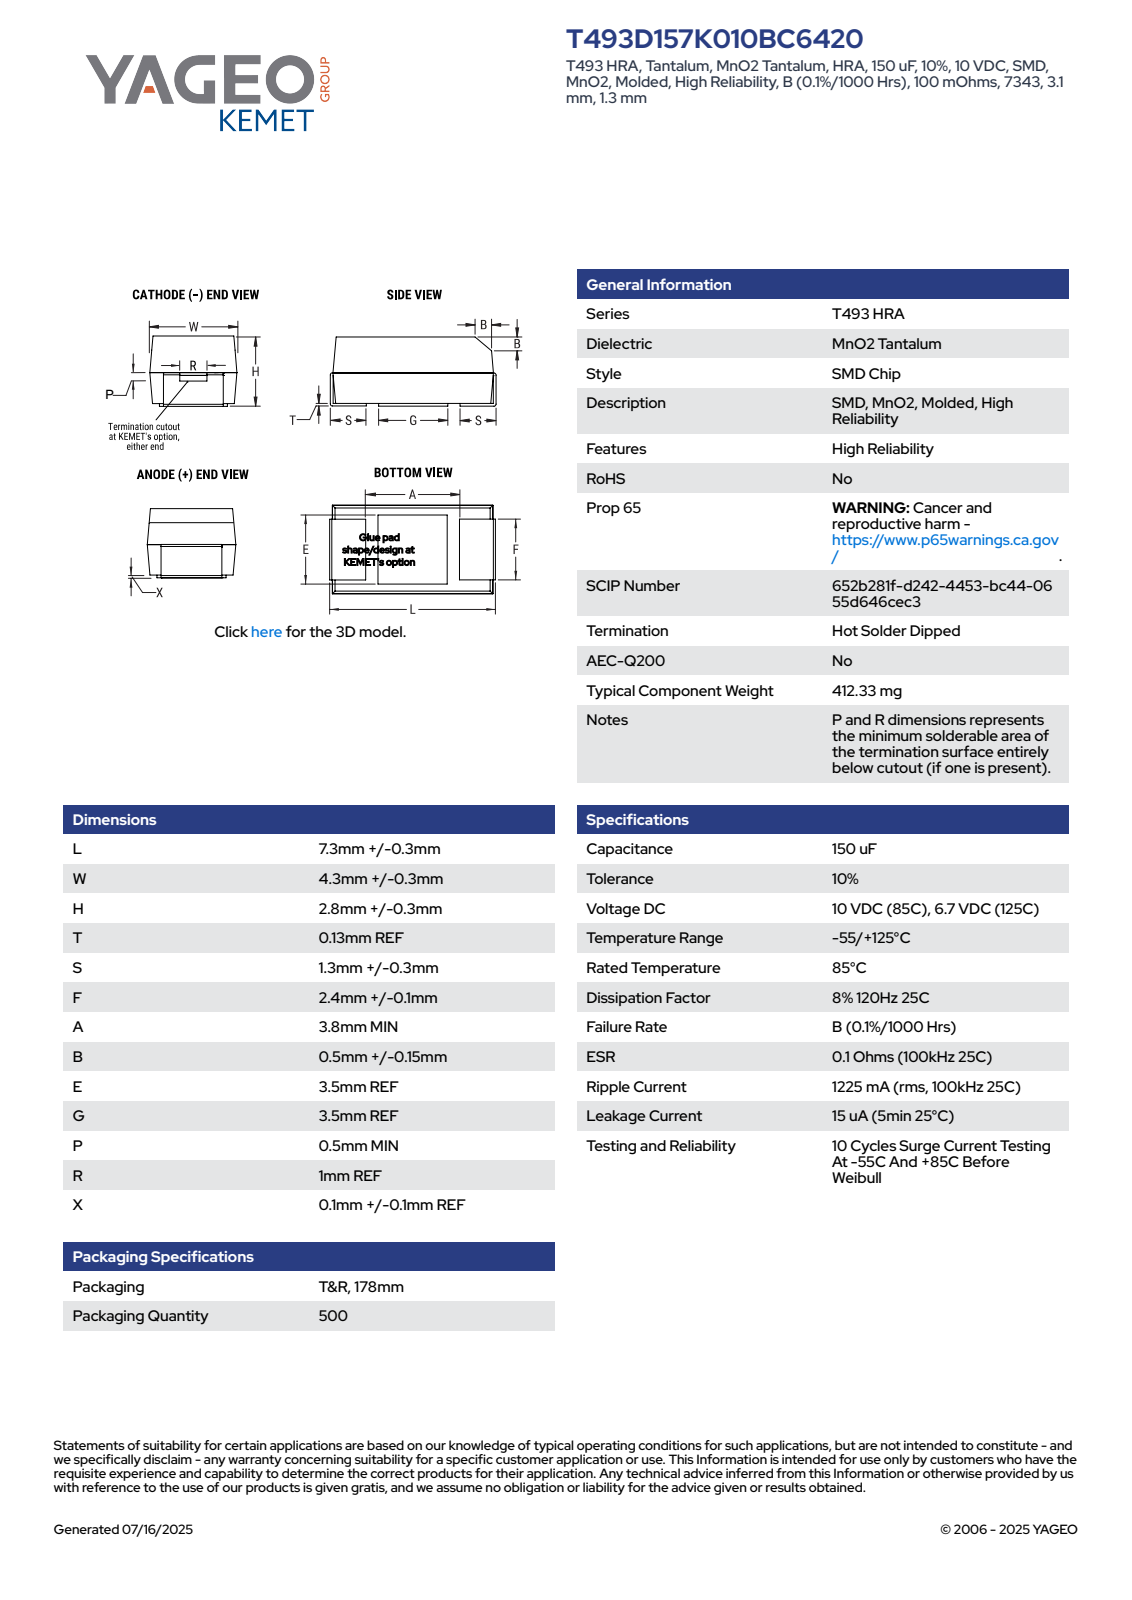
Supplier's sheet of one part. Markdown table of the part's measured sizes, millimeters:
| quantity | value |
| --- | --- |
| part name | CTSM_TCM2NK_7343_L7.6W4.6H3.1T0.13S1.3F2.5A3.8B0.65E3.5G3.5P0.5R1X0.2 |
| STEP written by | SolidWorks 2020 (AUTOMOTIVE_DESIGN) |
| units | millimeters |
| bodies | 4 solids, 100 faces (95 planar, 5 cylindrical, 0 other) |
| overall size | 7.6 × 4.6 × 3.1 |
| volume | 93 mm³ |
| surface area | 152 mm² |
| partial cylindrical surfaces (radius × count) | 0.1 × 4 |
| main face-to-face distances | 3.1, 2.9, 4.53, 4.54, 2.97, 7.47, 7.6, 7.34, 2.05, 5.55 |
